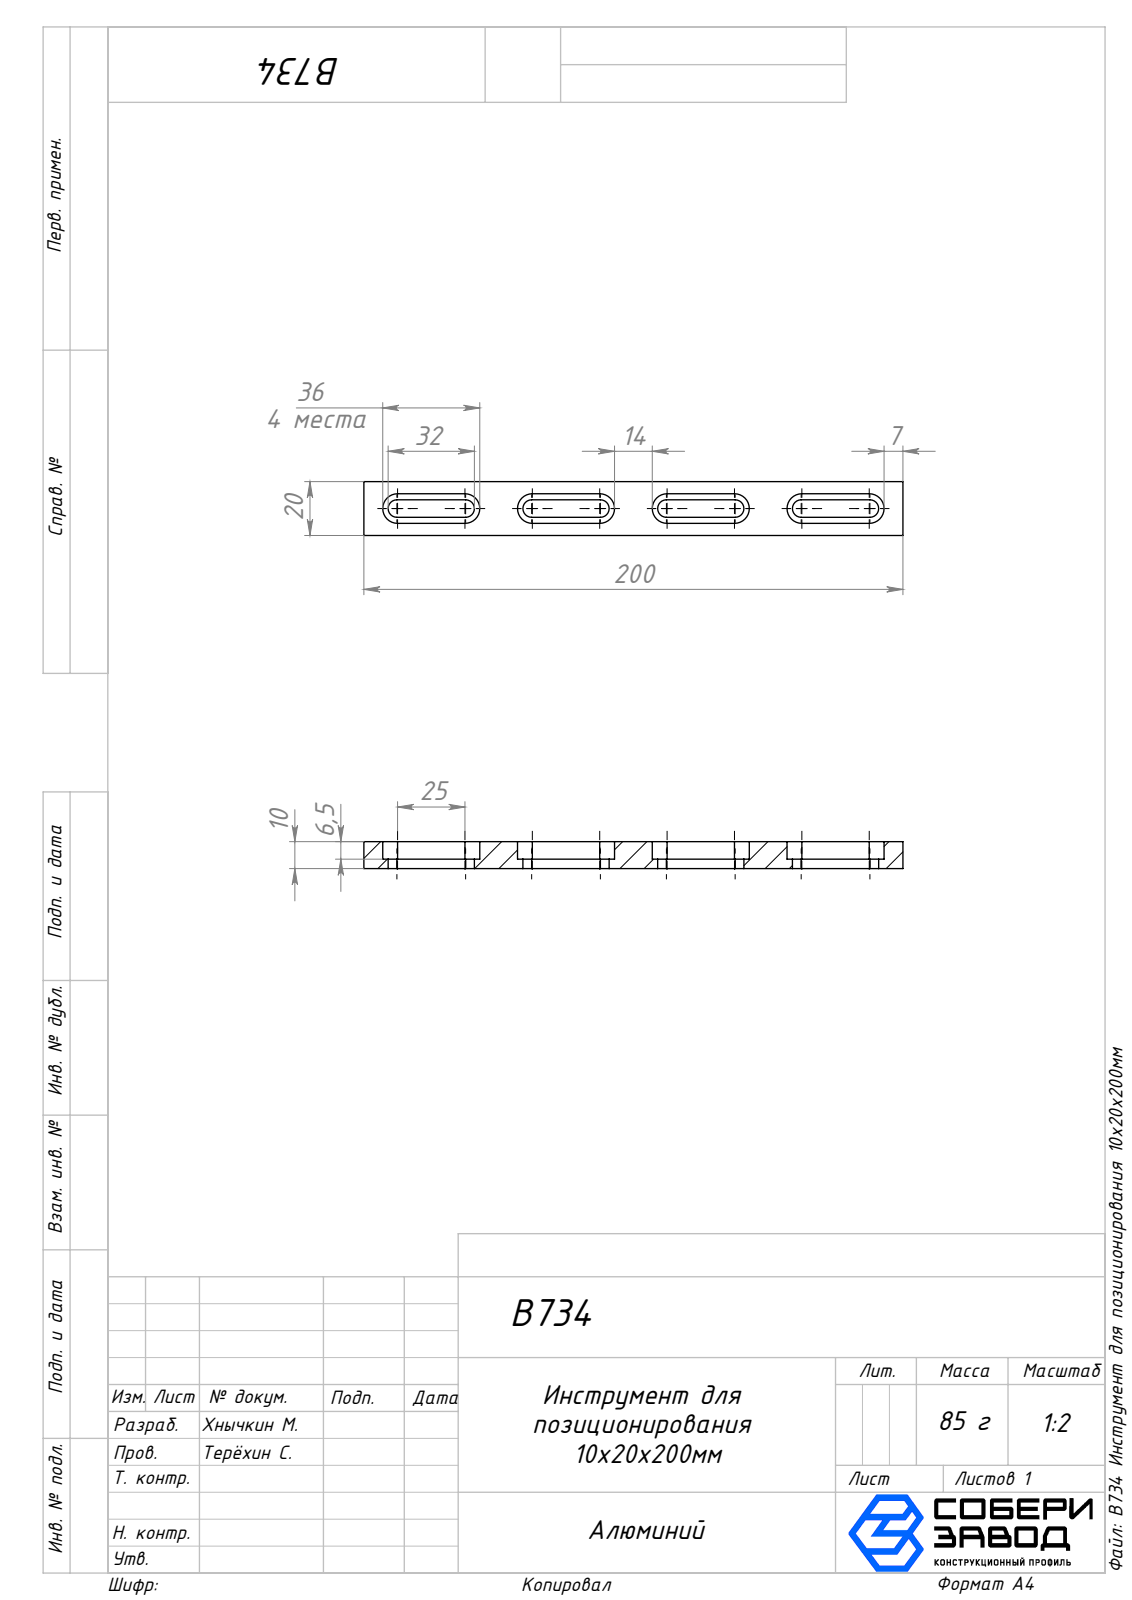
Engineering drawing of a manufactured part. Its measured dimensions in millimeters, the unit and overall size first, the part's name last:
Units: millimetres
Overall size (bounding box): 200 × 20 × 10
Partial cylindrical surfaces — rounded edges, fillets, slot ends (radius × count): R3.25 ×8, R5.5 ×8
Main face-to-face distances: 10, 20, 4.5, 15.5, 6.5, 6.75, 13.25, 2.25, 8.75, 3.5
Volume: 27 594 mm³ · Surface area: 14 007 mm²
Bodies: 1 solid, 42 faces (26 planar, 16 cylindrical, 0 other)
Part name (STEP PRODUCT): B734 Инструмент для позиционирования 10x20x200мм
STEP written by: SolidWorks 2025 (AUTOMOTIVE_DESIGN)
